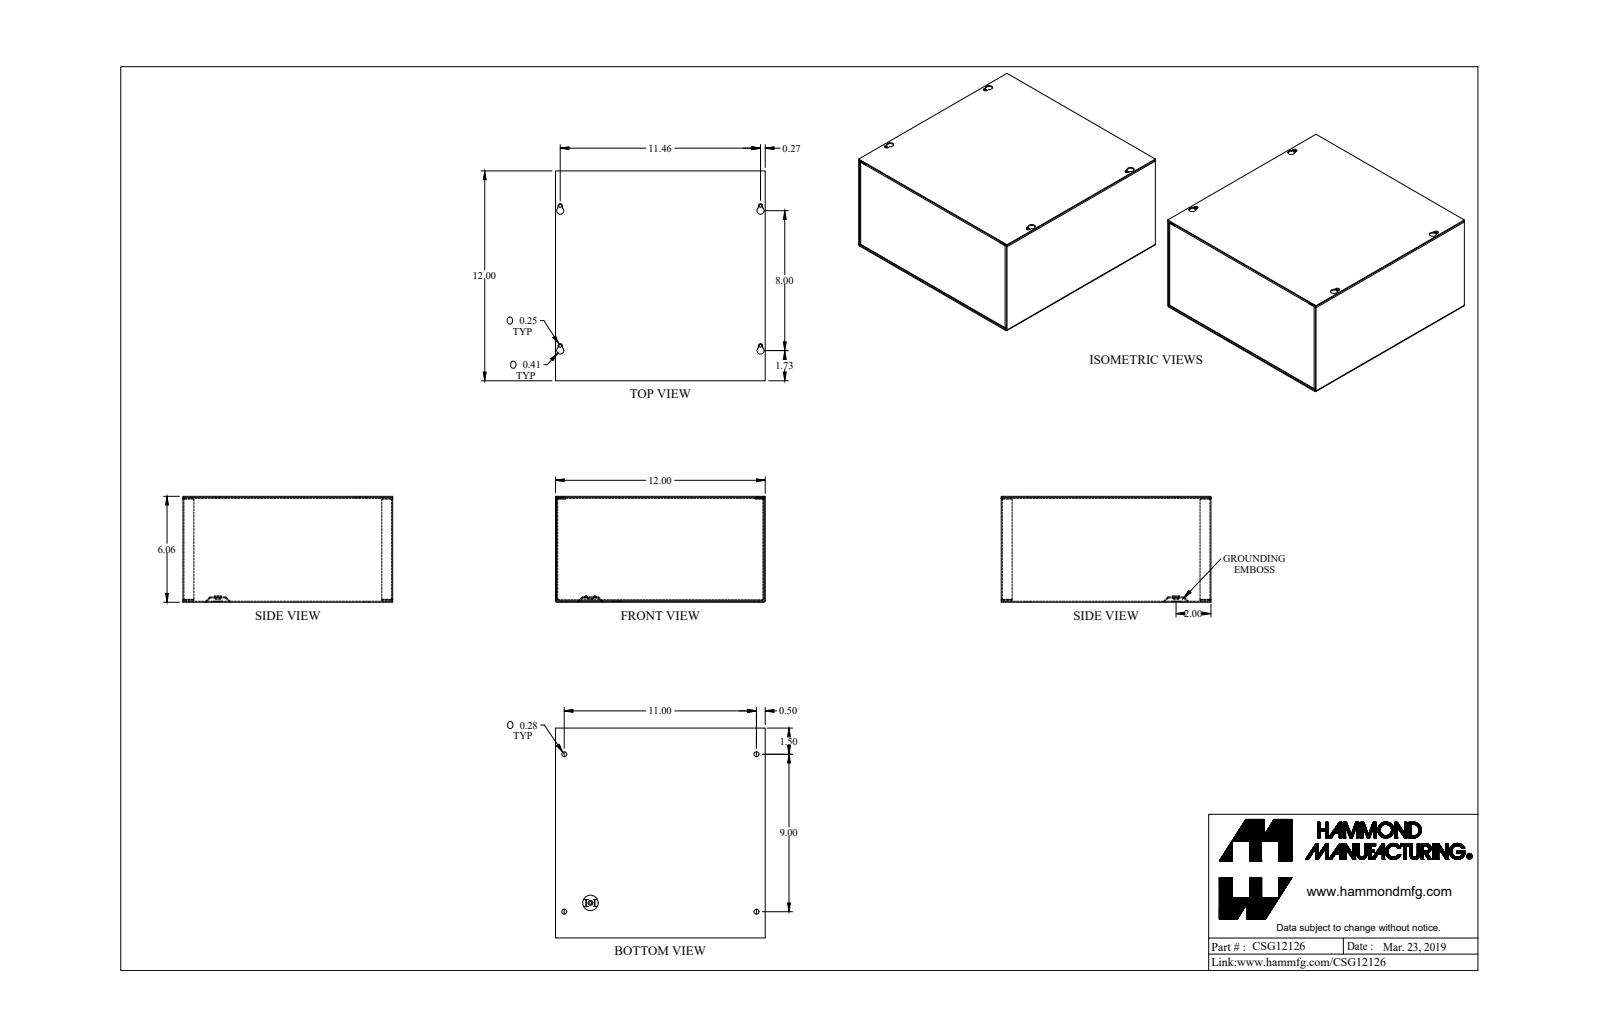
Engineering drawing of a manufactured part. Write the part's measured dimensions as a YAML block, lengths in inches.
part_name: "CSG12126_Default"
step_written_by: "SolidWorks 2019 (CONFIG_CONTROL_DESIGN)"
units: inches
bodies: {solids: 4, faces: 205, planar: 125, cylindrical: 72, other: 8}
overall_size: [12, 12, 6.057]
volume: 34.99
surface_area: 1240
round_holes:
  - {diameter: 0.17, count: 5}
  - {diameter: 0.281, count: 4}
  - {diameter: 0.5, count: 1}
round_bosses_or_shafts:
  - {diameter: 0.492, count: 1}
  - {diameter: 0.284, count: 1}
partial_cylinders:
  - {radius: 0.029, count: 12}
  - {radius: 0.086, count: 12}
  - {radius: 0.057, count: 8}
  - {radius: 0.125, count: 4}
  - {radius: 0.203, count: 4}
face_to_face_distances: [0.057, 6, 11.943, 5.943, 6.057, 12, 11.886, 0.08, 5.863, 5.92]
hole_center_spacings: [0.55, 8.503, 11.241, 14.084, 8, 9, 11, 11.46]
